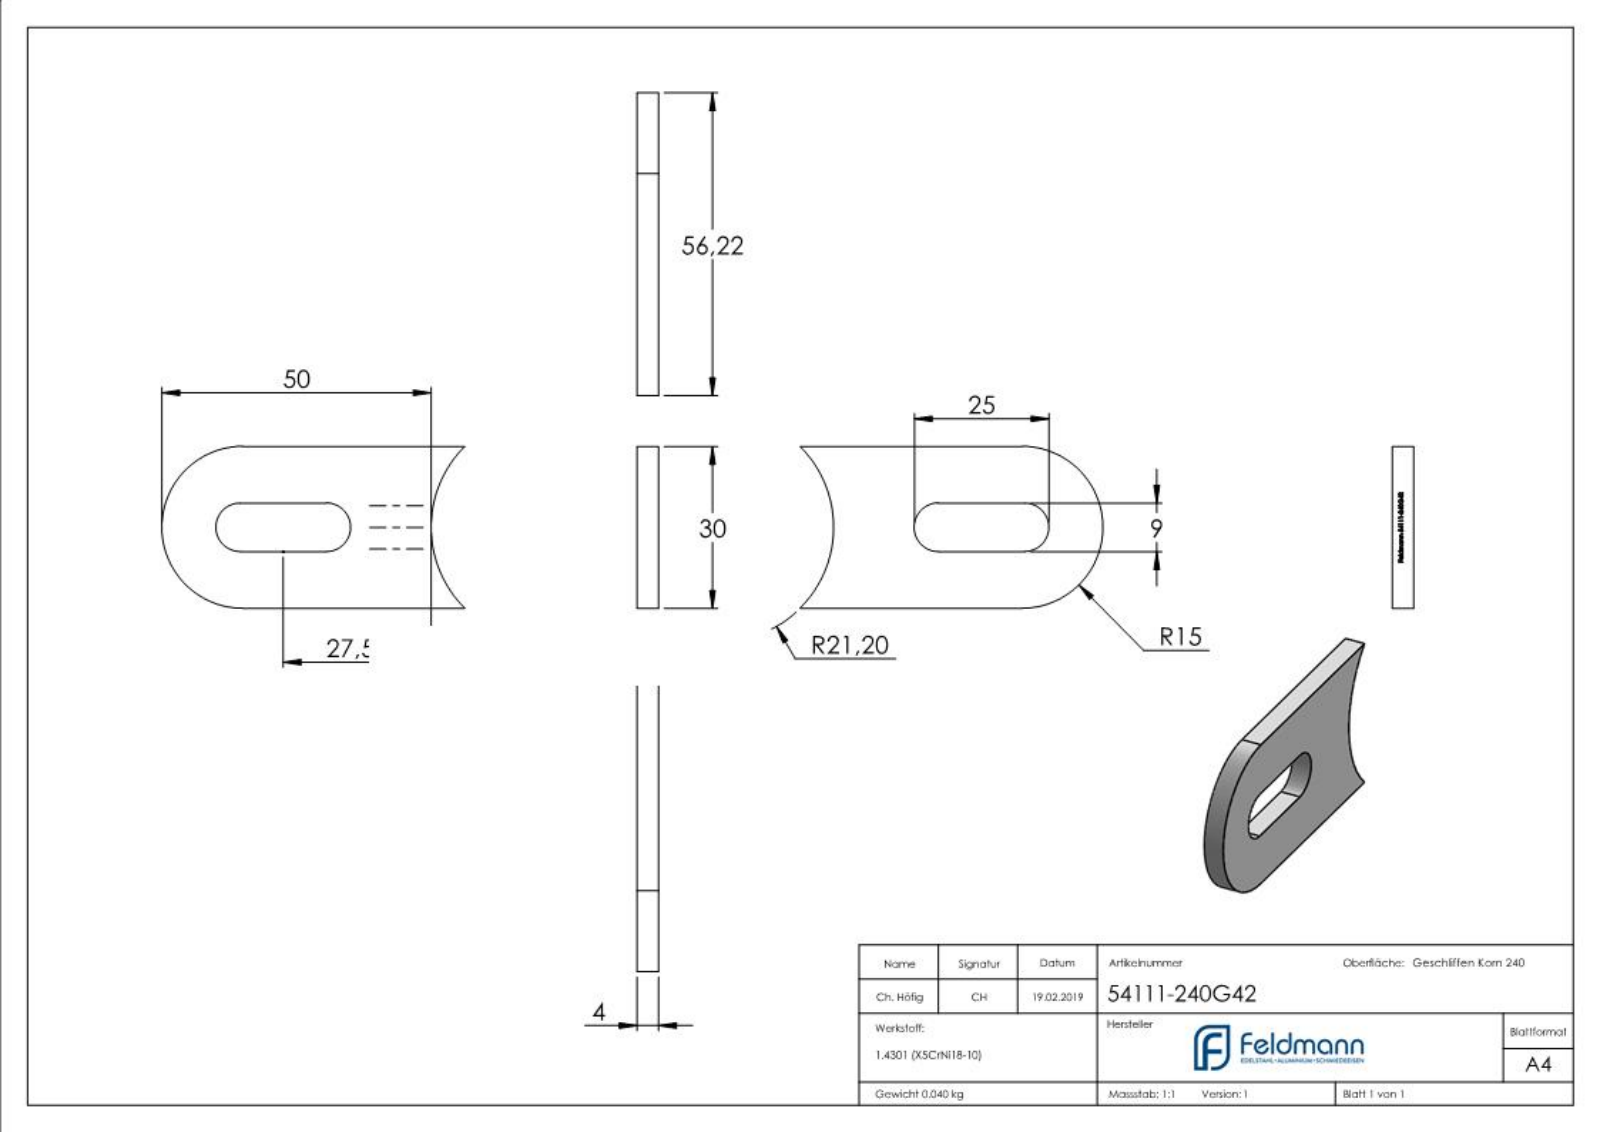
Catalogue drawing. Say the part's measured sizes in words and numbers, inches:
The part is named "54111-240G42". Its 3-D file was written by "SolidWorks 2015 (CONFIG_CONTROL_DESIGN)". It is 1 solid with 262 faces: 143 planar, 33 cylindrical and 86 other. Overall it measures 2.213 by 1.181 by 0.157 inches. Its volume is 0.306 cubic inches and its surface area 5.281 square inches. Partial cylindrical surfaces (rounded edges, fillets, slot ends): 2 of radius 0.177, 1 of radius 0.591, 1 of radius 0.835, 1 of radius 0.839. The main face-to-face distances are 0.157, 1.181, 0.413, 0.768, 0.354, 0.079, 0.024, 0.051, 0.021, 0.086.
